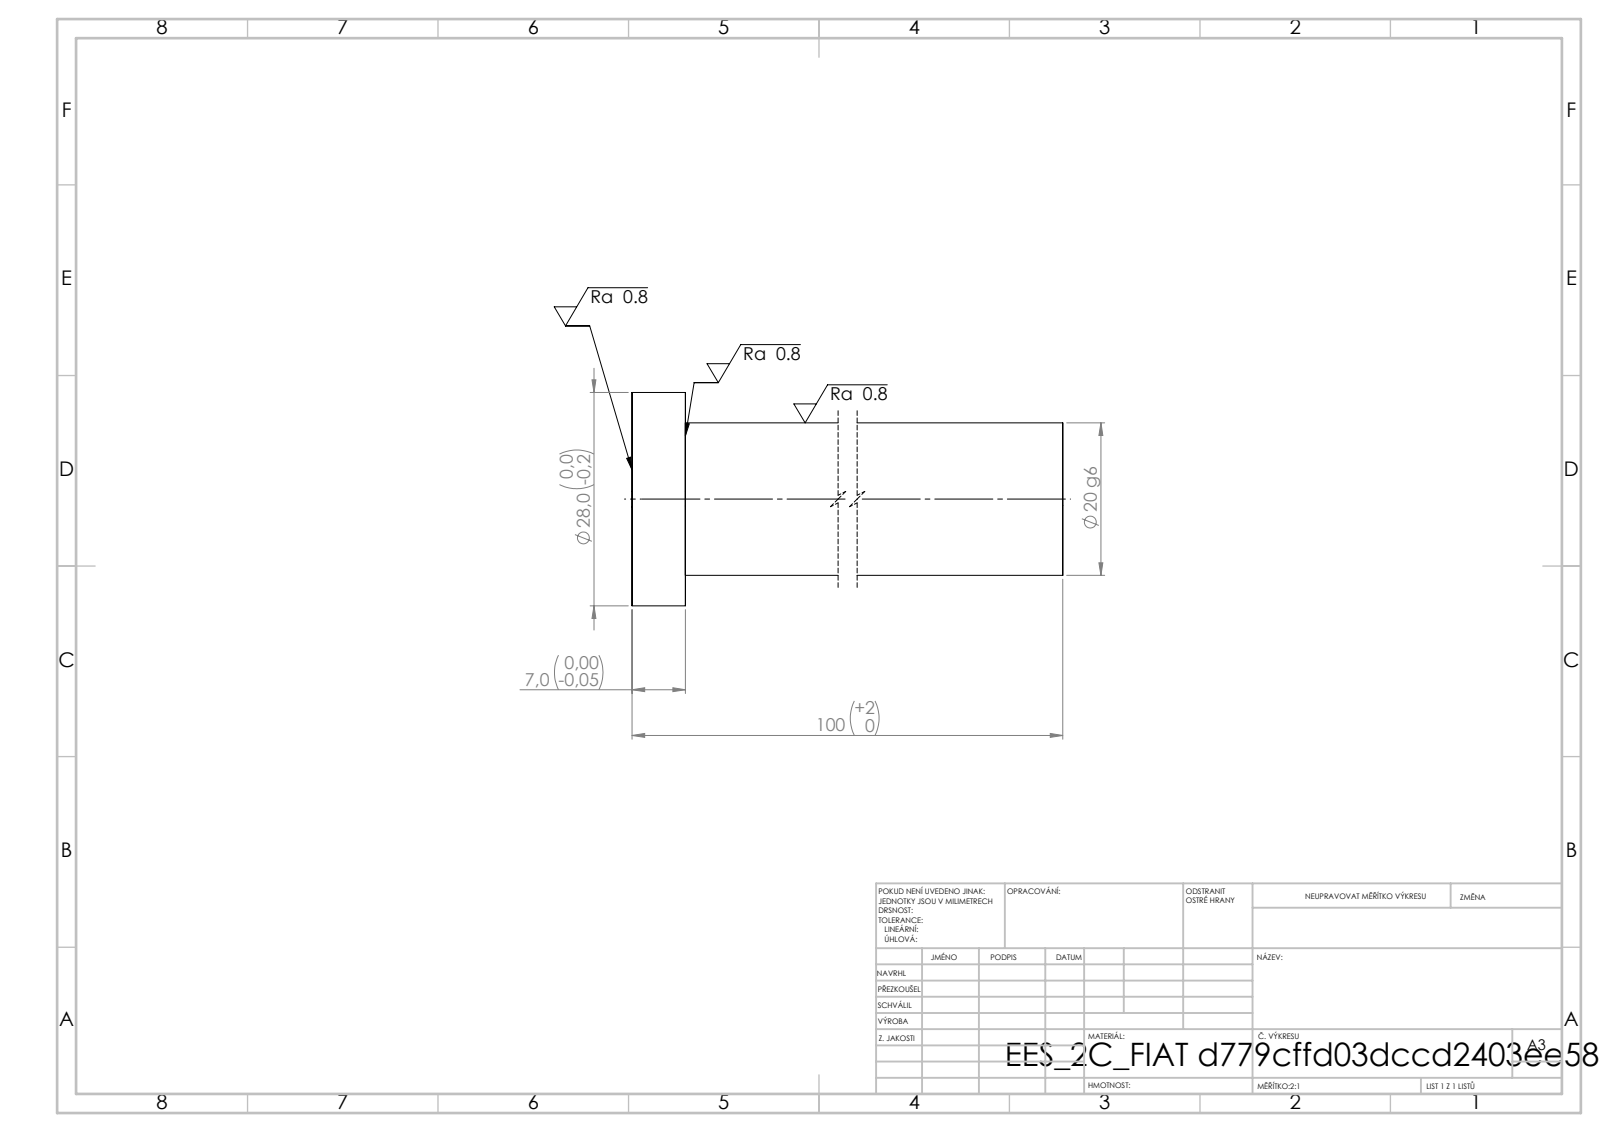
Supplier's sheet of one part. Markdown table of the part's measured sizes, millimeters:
| quantity | value |
| --- | --- |
| STEP written by | SolidWorks 2019 (CONFIG_CONTROL_DESIGN) |
| units | millimeters |
| bodies | 1 solid, 7 faces (3 planar, 4 cylindrical, 0 other) |
| overall size | 100 × 28 × 28 |
| volume | 33 527 mm³ |
| surface area | 7 691 mm² |
| round bosses / shafts (diameter × count) | 28 × 1, 20 × 1 |
| main face-to-face distances | 100, 7, 93 |
